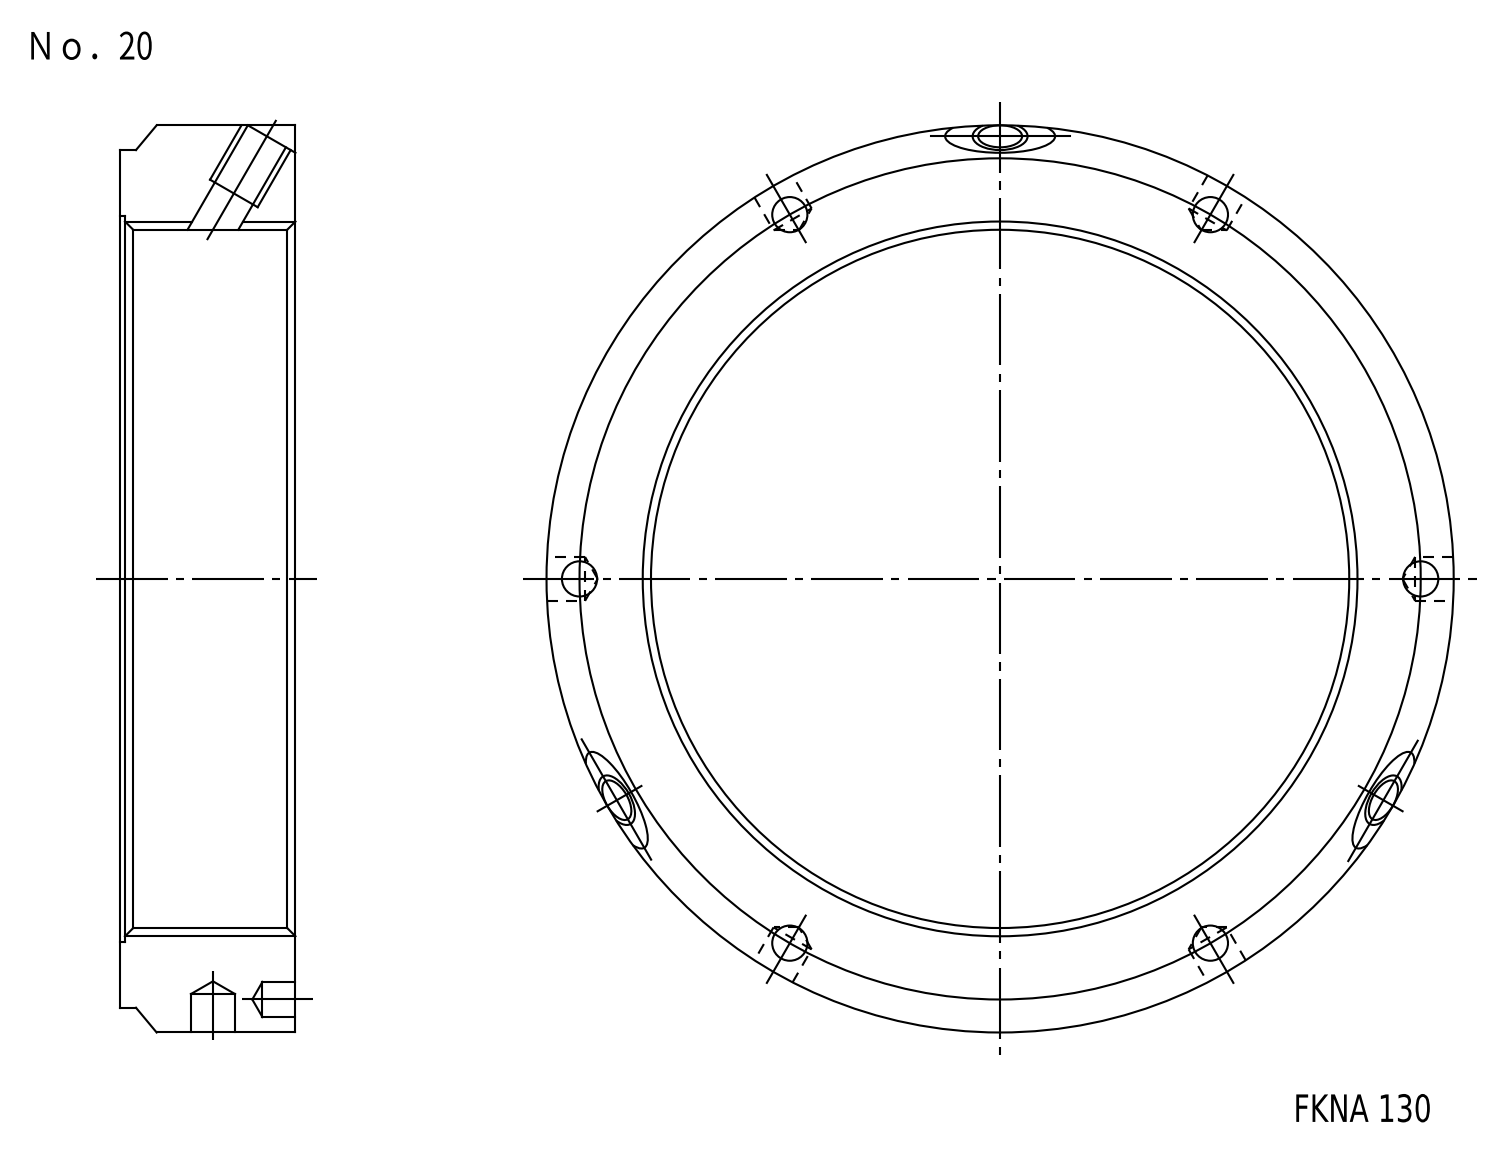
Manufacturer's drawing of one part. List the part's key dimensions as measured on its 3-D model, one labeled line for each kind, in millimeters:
Part name (STEP PRODUCT): FKD FKNA130
STEP written by: Autodesk Inventor LT (CONFIG_CONTROL_DESIGN)
Units: millimetres
Bodies: 1 solid, 44 faces (6 planar, 25 cylindrical, 13 other)
Overall size (bounding box): 165 × 165 × 32
Volume: 246 290 mm³ · Surface area: 47 330 mm²
Round holes (diameter × count): ⌀6.4 ×6, ⌀8 ×3, ⌀8.38 ×3, ⌀10.2 ×3, ⌀130 ×1, ⌀132 ×1
Round bosses / shafts (diameter × count): ⌀165 ×1, ⌀156 ×1
Partial cylindrical surfaces — rounded edges, fillets, slot ends (radius × count): R20 ×3
Main face-to-face distances: 32, 1.5, 30.5
Hole centre spacings: 76.5, 132.5, 153
